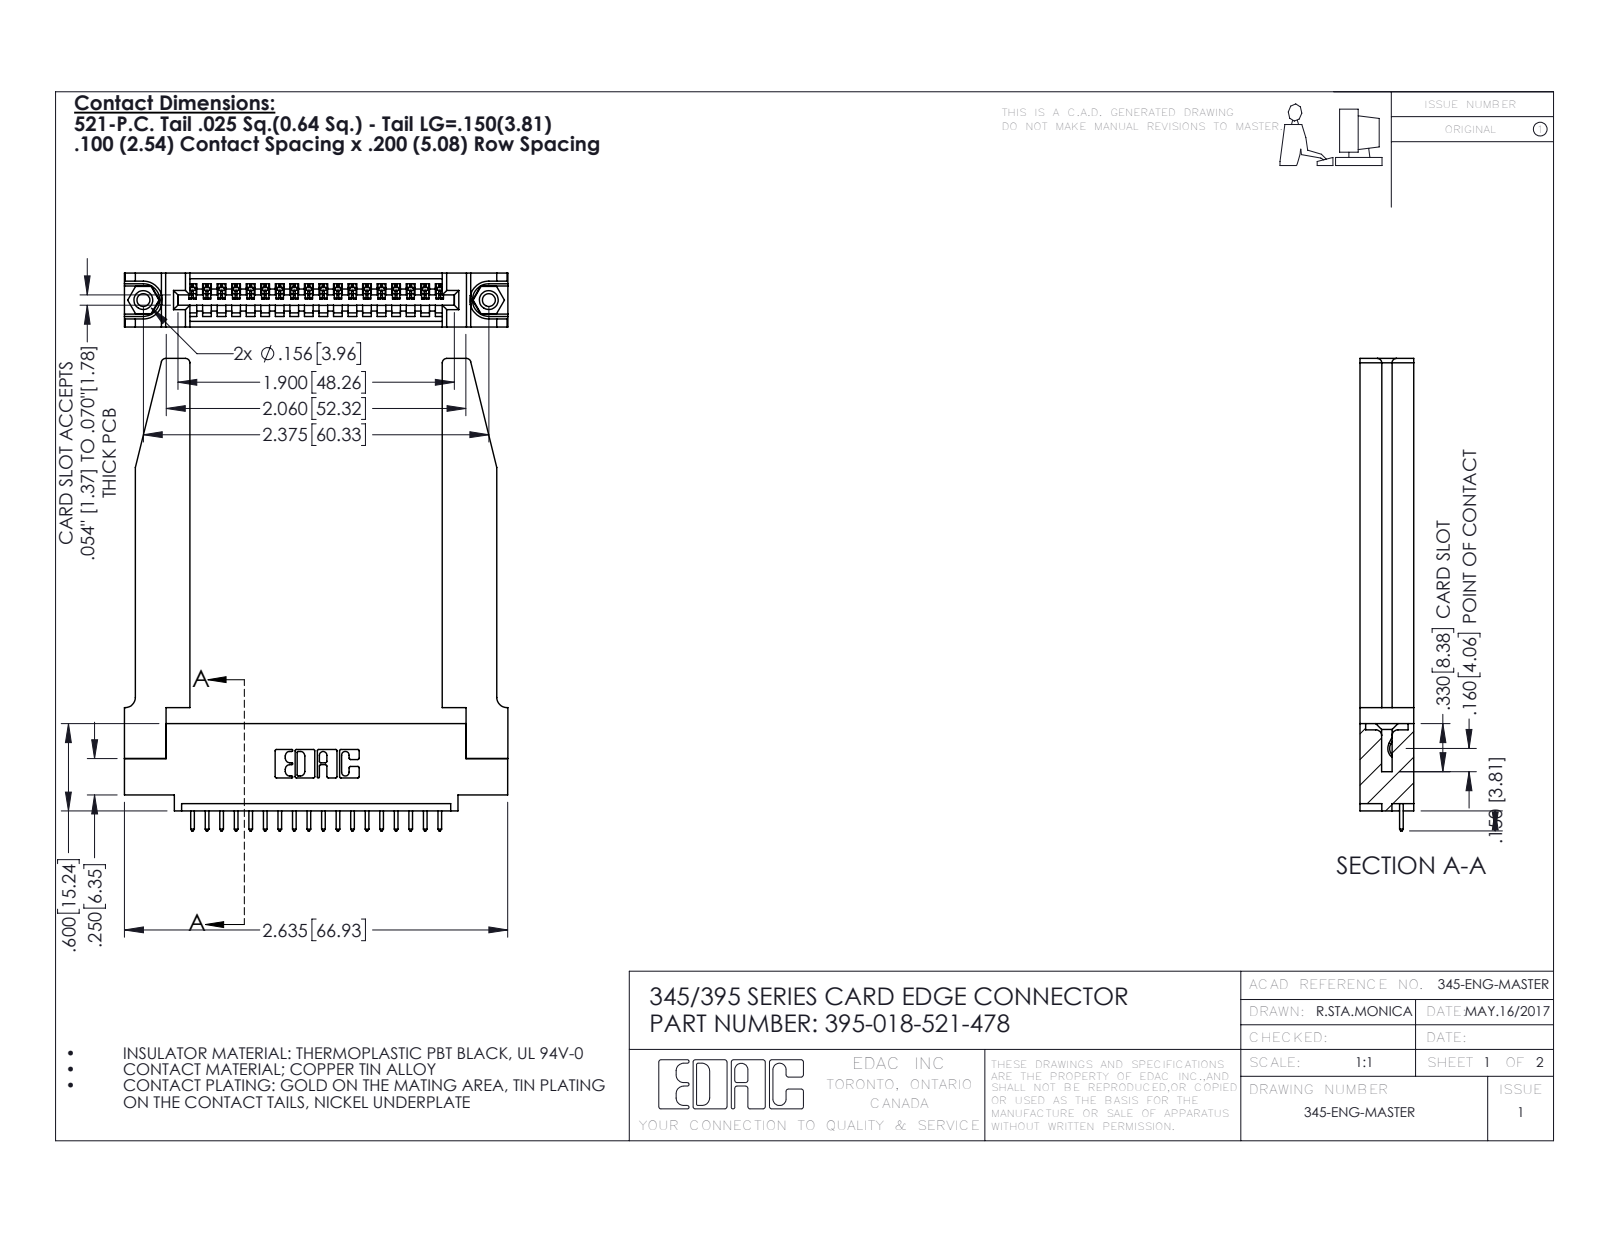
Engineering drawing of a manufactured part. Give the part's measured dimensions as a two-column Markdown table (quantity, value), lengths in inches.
| quantity | value |
| --- | --- |
| part name | 395-018-521-478; 345-292-001_345-293-121; 345 Part_0.110 Offset - 0.156 Dia-TH; 345-250-001_345-250-001-102 (+1 more) |
| STEP written by | SolidWorks 2016 (CONFIG_CONTROL_DESIGN) |
| units | inches |
| bodies | 23 solids, 1408 faces (946 planar, 410 cylindrical, 52 other) |
| overall size | 3.247 × 2.636 × 0.37 |
| volume | 0.843 in³ |
| surface area | 22.36 in² |
| round holes (diameter × count) | 0.089 × 2, 0.125 × 2, 0.156 × 2, 0.064 × 1 |
| round bosses / shafts (diameter × count) | 0.155 × 2 |
| partial cylindrical surfaces (radius × count) | 0.006 × 36, 0.01 × 36, 0.01 × 22, 0.03 × 8, 0.007 × 6, 0.031 × 6, 0.026 × 3, 0.031 × 2 |
| main face-to-face distances | 0.37, 0.072, 0.298, 0.15, 0.148, 0.2, 0.098, 0.272, 0.025, 0.22 |
| hole center spacings | 0.27, 2.141, 2.375 |
